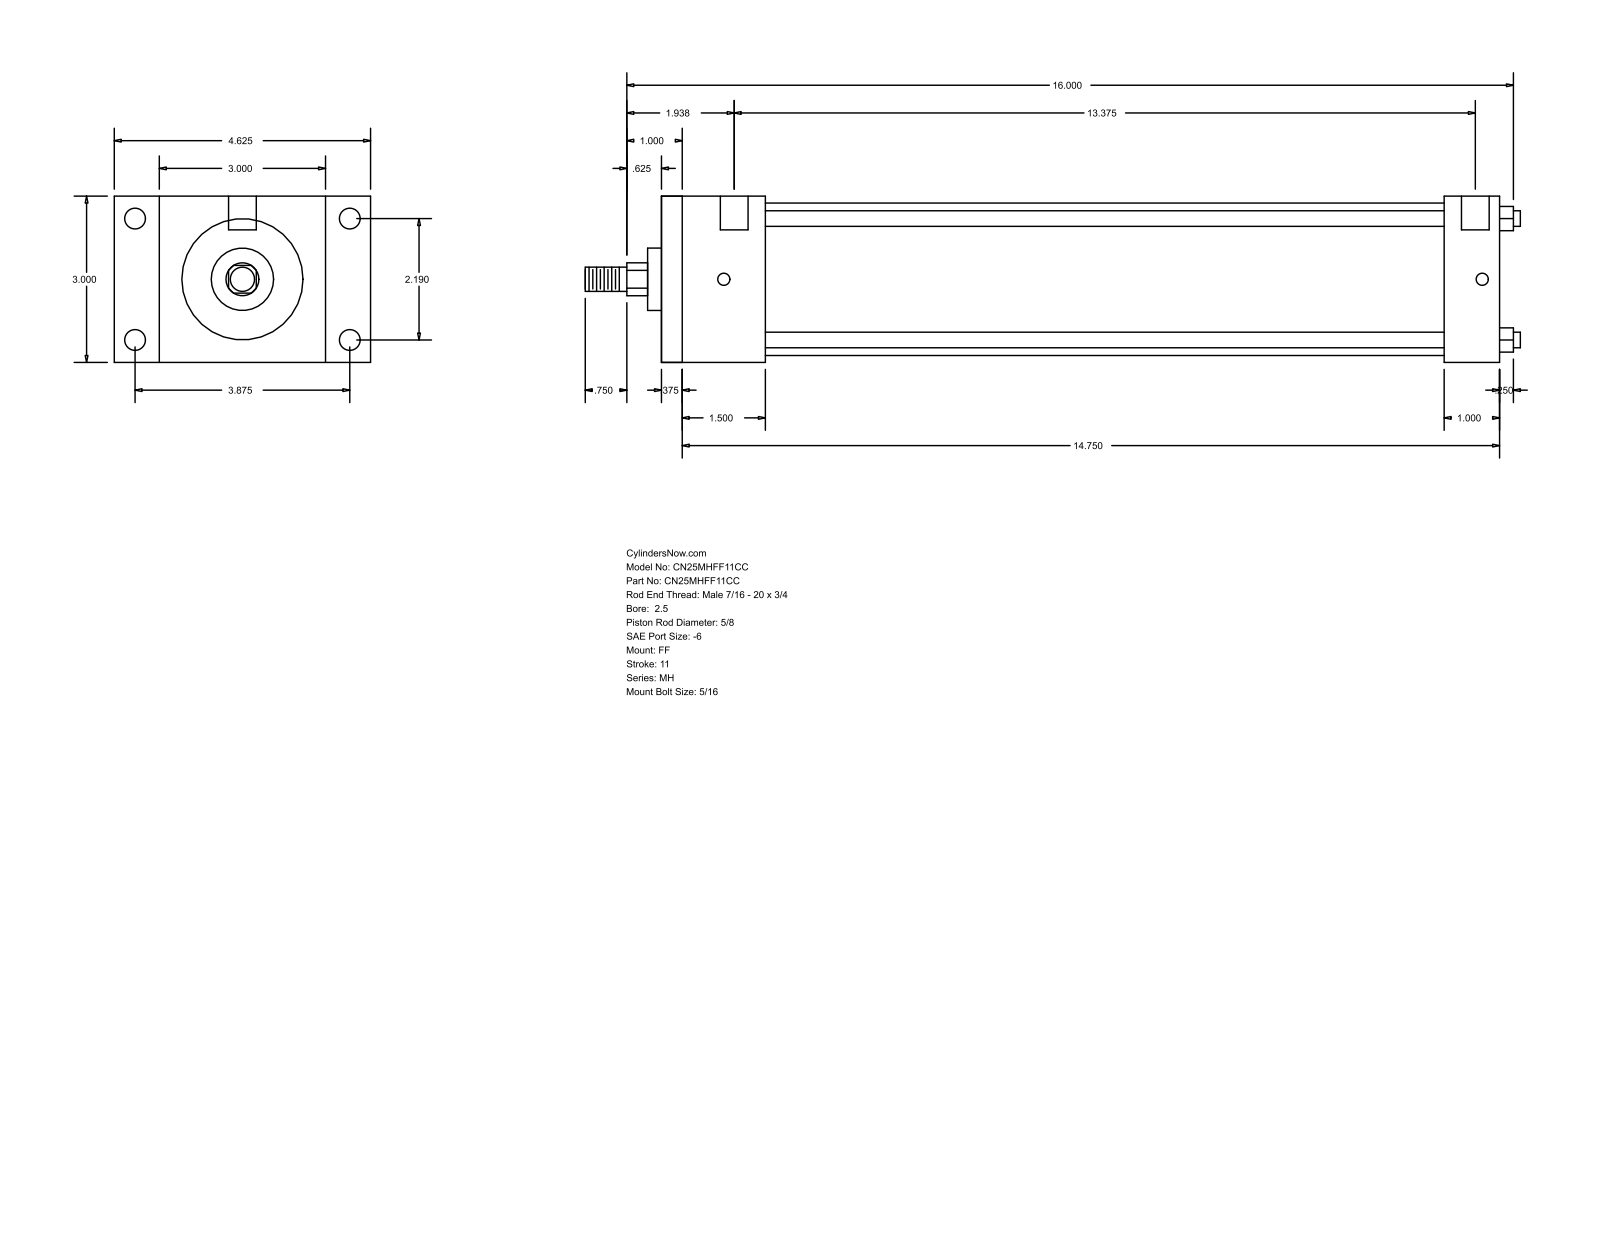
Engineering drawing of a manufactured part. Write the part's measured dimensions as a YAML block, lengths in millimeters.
part_name: "MH_FF__0250_0.625"
step_written_by: "GSSL Pune (CONFIG_CONTROL_DESIGN)"
units: millimeters
bodies: {solids: 0, faces: 92, planar: 64, cylindrical: 28, other: 0}
overall_size: [428.62, 117.47, 76.2]
round_holes:
  - {diameter: 5.56, count: 4}
  - {diameter: 9.53, count: 4}
  - {diameter: 12.7, count: 2}
round_bosses_or_shafts:
  - {diameter: 7.14, count: 4}
  - {diameter: 69.85, count: 1}
  - {diameter: 28.57, count: 1}
  - {diameter: 15.88, count: 1}
  - {diameter: 11.11, count: 1}
partial_cylinders:
  - {radius: 7.54, count: 1}
face_to_face_distances: [76.2, 384.17, 9.52, 374.65, 25.4, 47.62, 358.77, 38.1, 349.25, 311.15]
hole_center_spacings: [55.62, 98.42, 113.05, 347.66, 3.17, 4.76, 339.73, 342.9]
